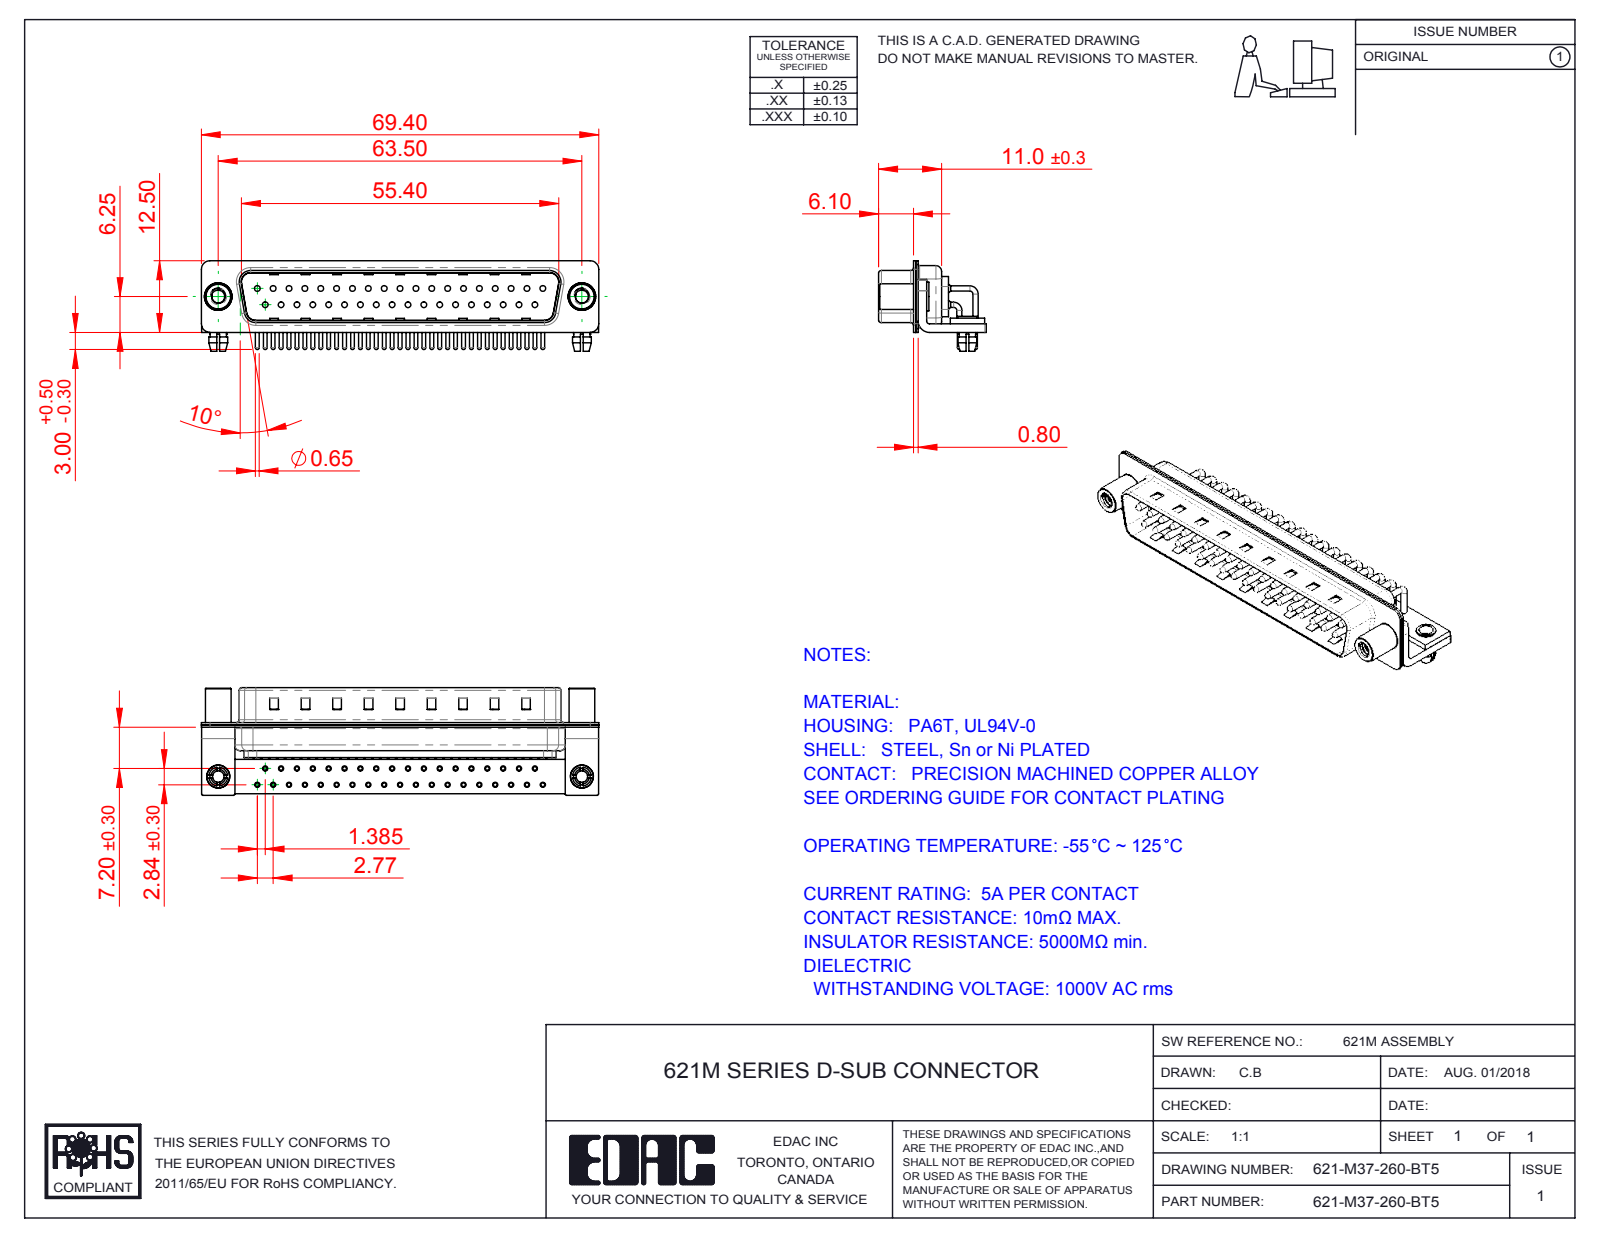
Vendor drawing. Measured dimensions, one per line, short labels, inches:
name: 621M Contact Row 1; 621M Board Lock; 621M Shell Front_37 Contacts; 621M Contact Row 2 (+6 more)
written by: SolidWorks 2016 (CONFIG_CONTROL_DESIGN)
unit: in
bodies: 47 solids, 4748 faces (2647 planar, 1643 cylindrical, 458 other)
size: 2.732 × 0.74 × 0.622
volume: 0.291 in³; area: 19.34 in²
holes: 39× ⌀0.079, 37× ⌀0.035, 37× ⌀0.039, 37× ⌀0.067, 2× ⌀0.089, 2× ⌀0.098, 2× ⌀0.126, 2× ⌀0.157, 2× ⌀0.189
bosses: 46× ⌀0.035, 37× ⌀0.059, 37× ⌀0.026, 2× ⌀0.197, 2× ⌀0.193, 2× ⌀0.177, 2× ⌀0.157, 2× ⌀0.134
rounds: 37× R0.04, 16× R0.01, 16× R0.059, 13× R0.079, 9× R0.02, 8× R0.063, 4× R0.024, 4× R0.026
face distances: 0.016, 0.033, 0.049, 0.376, 0.059, 0.409, 0.327, 0.031, 0.343, 0.039
hole spacings: 0.124, 0.109, 0.218, 0.327, 0.436, 0.545, 0.198, 0.654
